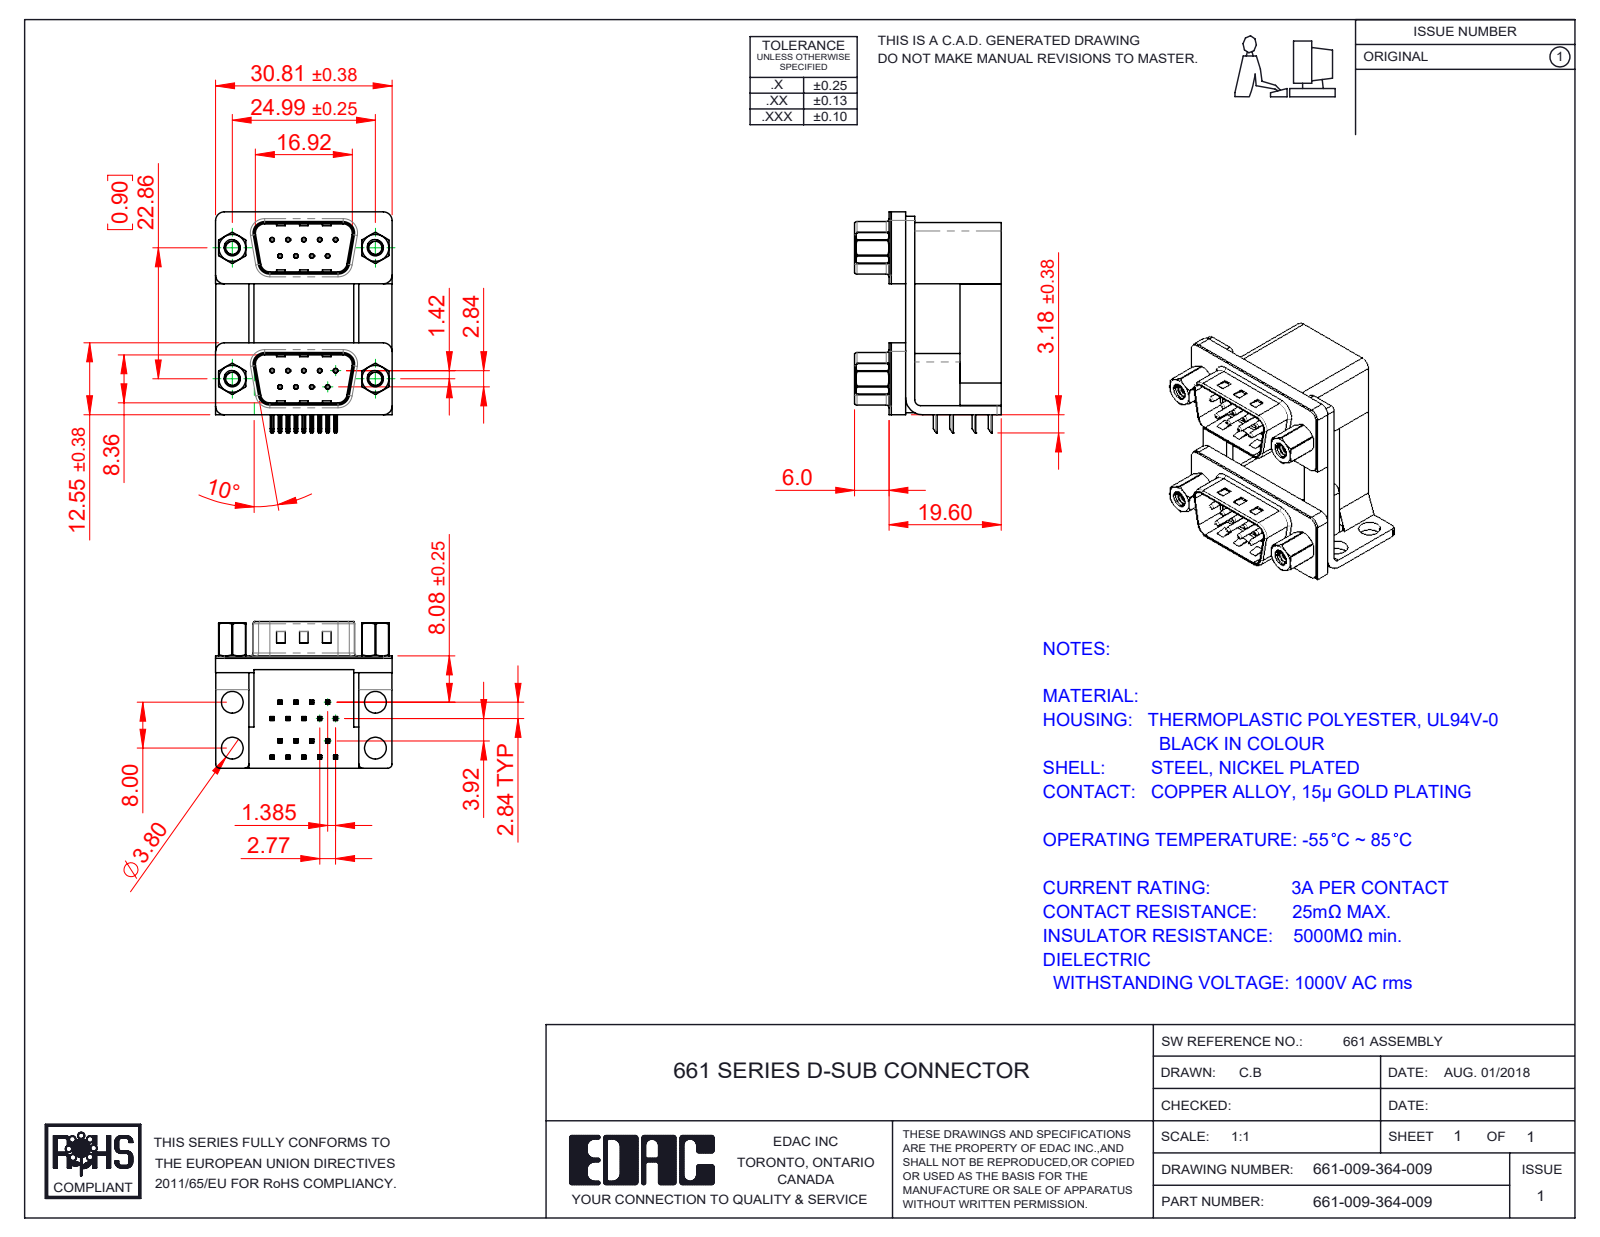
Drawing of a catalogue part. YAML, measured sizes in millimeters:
part_name: "661 Contact Top Lower; 661 Contact Bottom Upper_H; 661 Mounting Bracket_NoneH; 661 Shell_09 Contacts (+8 more)"
step_written_by: "SolidWorks 2020 (CONFIG_CONTROL_DESIGN)"
units: millimeters
bodies: {solids: 33, faces: 2200, planar: 1196, cylindrical: 738, other: 266}
overall_size: [38.59, 30.81, 25.6]
volume: 11235
surface_area: 13250
round_holes:
  - {diameter: 0.35, count: 18}
  - {diameter: 0.8, count: 18}
  - {diameter: 2.26, count: 4}
  - {diameter: 2.29, count: 4}
  - {diameter: 3.5, count: 4}
  - {diameter: 3.8, count: 4}
  - {diameter: 4, count: 4}
  - {diameter: 4.8, count: 4}
  - {diameter: 5, count: 4}
round_bosses_or_shafts:
  - {diameter: 0.75, count: 18}
  - {diameter: 4.9, count: 4}
  - {diameter: 4.75, count: 4}
  - {diameter: 3.9, count: 4}
  - {diameter: 2.79, count: 4}
partial_cylinders:
  - {radius: 0.25, count: 72}
  - {radius: 0.12, count: 36}
  - {radius: 0.5, count: 16}
  - {radius: 1.5, count: 14}
  - {radius: 0.75, count: 8}
  - {radius: 0.9, count: 8}
  - {radius: 1.6, count: 8}
  - {radius: 2, count: 8}
face_to_face_distances: [0.4, 2.5, 22.86, 12, 16.7, 19.2, 12.4, 7.2, 9.5, 1.6]
hole_center_spacings: [3.16, 2.77, 23.03, 22.86, 5.54, 23.52, 20.07, 25.74]
